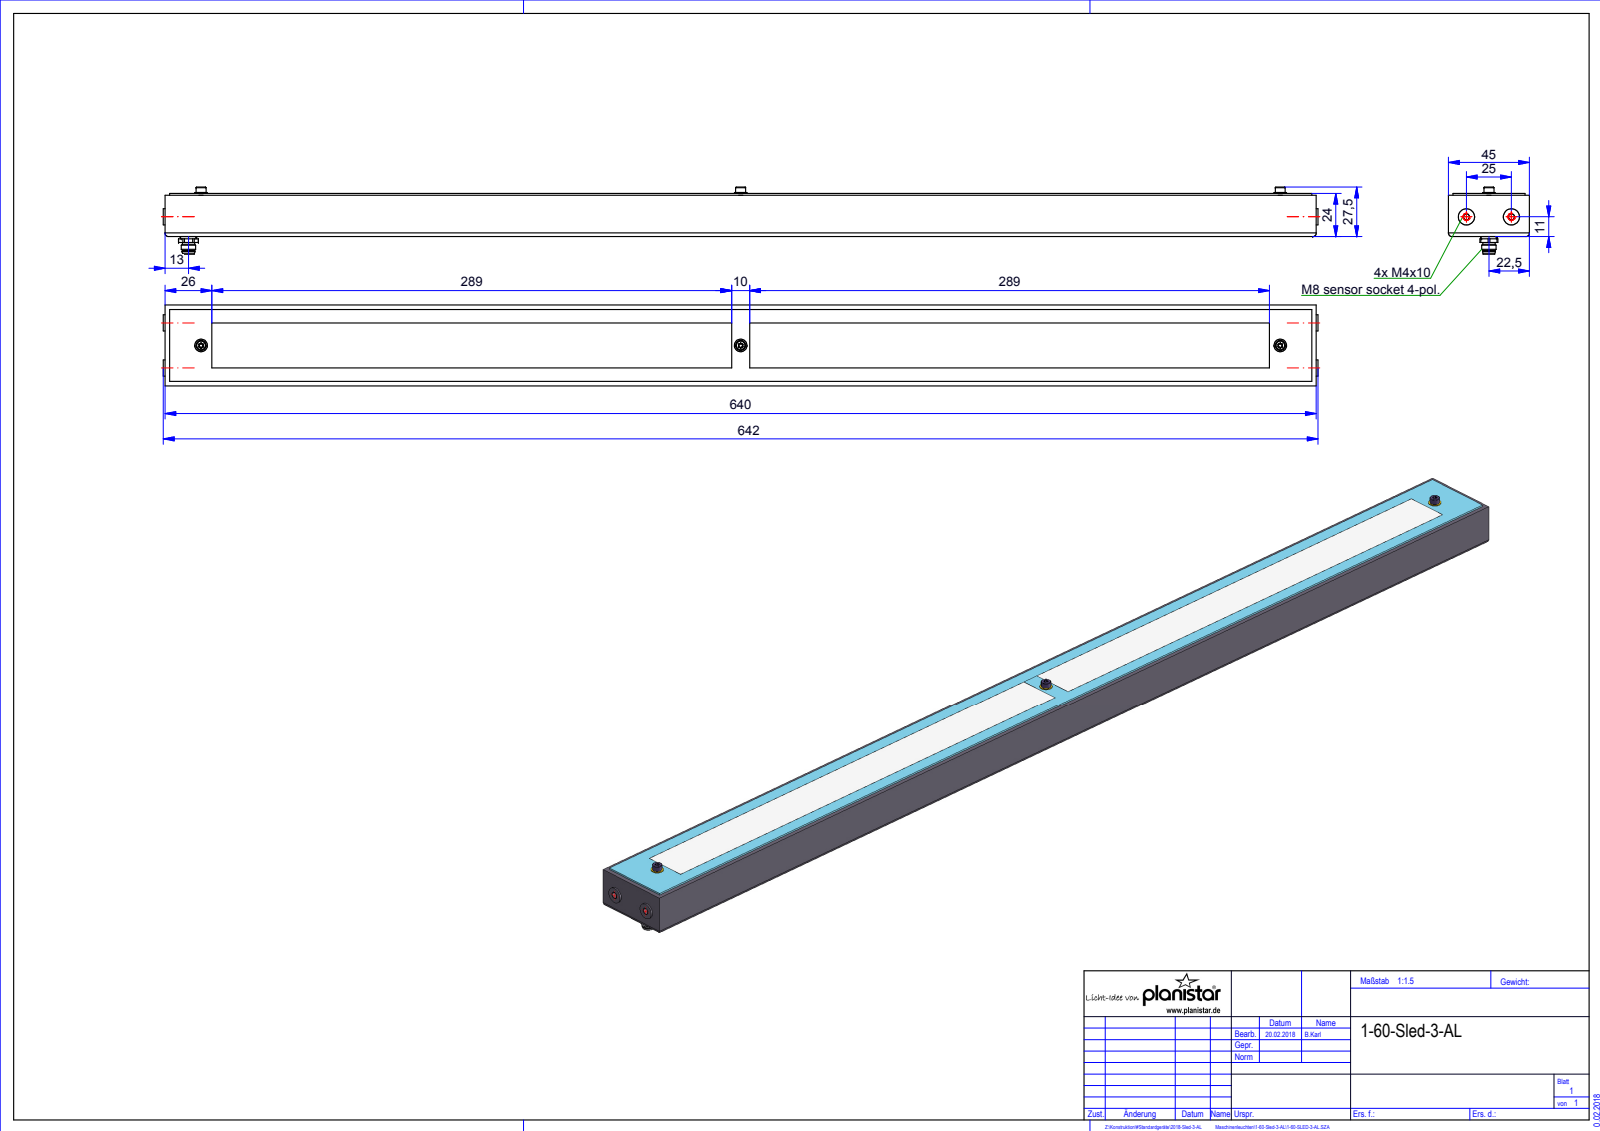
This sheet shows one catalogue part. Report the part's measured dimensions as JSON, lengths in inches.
{"part_name": "Root; Baugruppe_Xled-2-VD; QUADER_0; 09-3391-00-04 (+2 more)", "step_written_by": "HiCAD 2015 2002.1 Build 408 (AUTOMOTIVE_DESIGN)", "units": "inches", "bodies": {"solids": 8, "faces": 162, "planar": 59, "cylindrical": 84, "other": 19}, "overall_size": [25.276, 1.772, 1.465], "volume_in3": 41.88, "surface_area_in2": 142, "round_holes": [[0.126, 3], [0.13, 2], [0.157, 2], [0.228, 1]], "round_bosses_or_shafts": [[0.039, 4], [0.276, 3], [0.217, 3], [0.118, 3], [0.097, 3], [0.354, 2], [0.315, 1], [0.283, 1]], "partial_cylinders_radius": [[0.009, 18], [0.023, 18], [0.079, 4], [0.217, 1]], "face_to_face_distances": [0.943, 1.772, 0.945, 0.039, 0.906, 0.037, 0.098, 1.673, 25.197, 1.575], "hole_center_spacings": [11.811, 0.276, 0.984, 12.087, 23.622, 23.898]}
